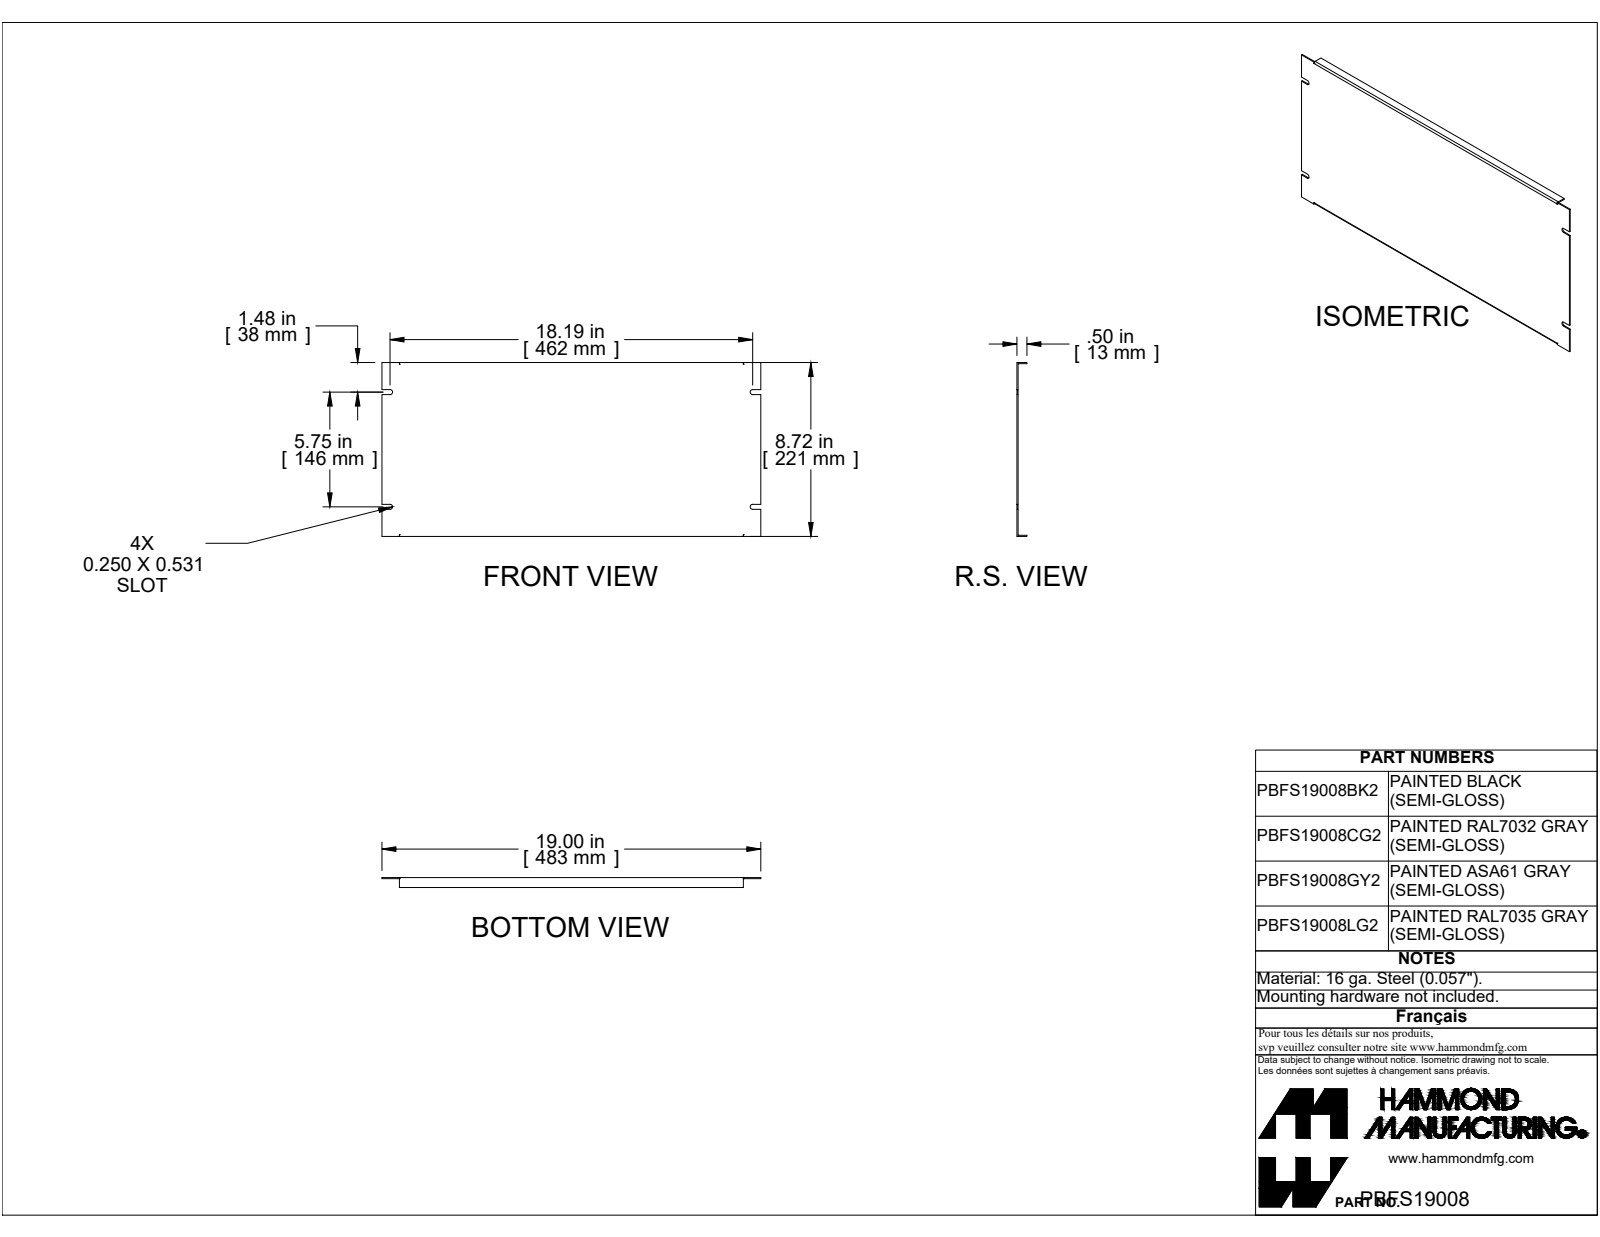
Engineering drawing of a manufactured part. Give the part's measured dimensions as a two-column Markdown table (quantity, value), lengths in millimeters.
| quantity | value |
| --- | --- |
| part name | PBFS19008 |
| STEP written by | SolidWorks 2019 (CONFIG_CONTROL_DESIGN) |
| units | millimeters |
| bodies | 1 solid, 46 faces (38 planar, 8 cylindrical, 0 other) |
| overall size | 482.6 × 221.4 × 12.7 |
| volume | 167 800 mm³ |
| surface area | 234 000 mm² |
| partial cylindrical surfaces (radius × count) | 3.2 × 4, 0.7 × 2, 2.2 × 2 |
| main face-to-face distances | 1.4, 220, 221.4, 218.5, 12.7, 11.3, 482.6, 22.2, 460.4, 34.5 |
